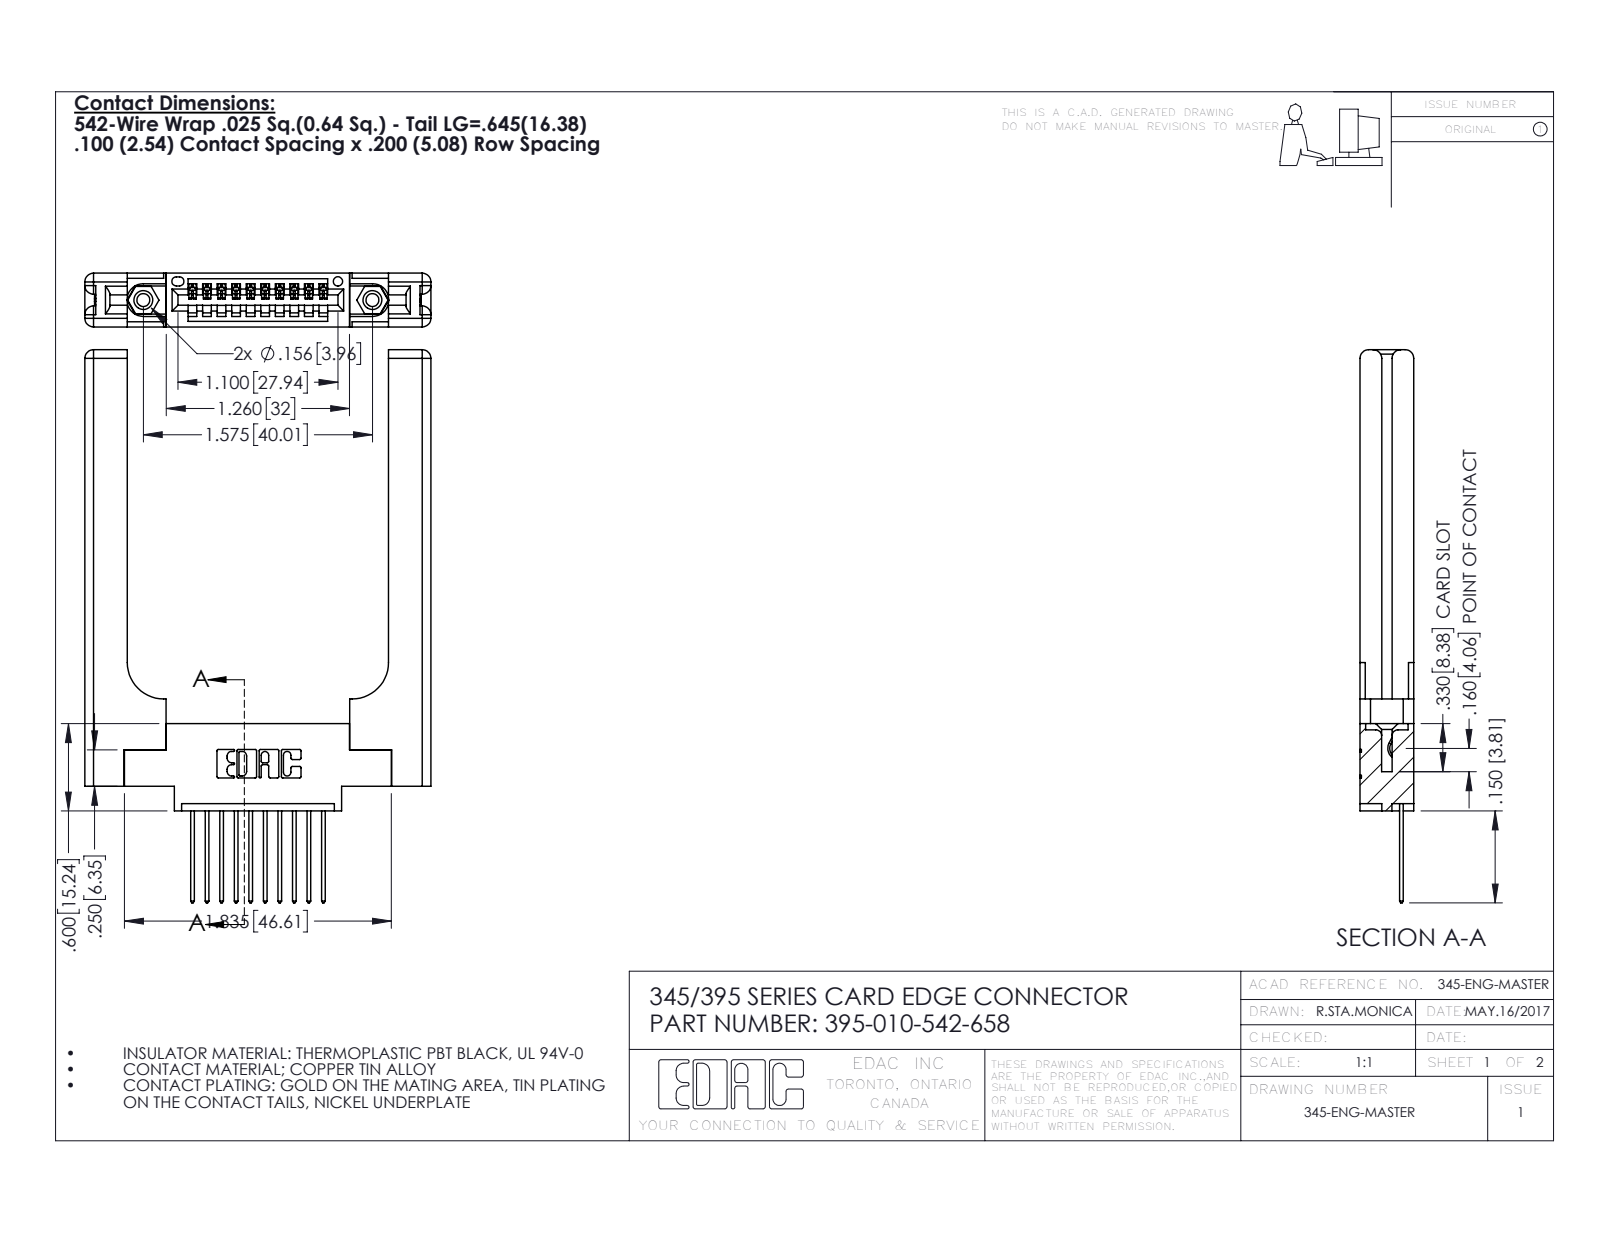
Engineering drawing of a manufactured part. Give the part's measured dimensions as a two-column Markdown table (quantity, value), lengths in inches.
| quantity | value |
| --- | --- |
| part name | 345-250-001_345-250-001-102; 395-010-542-658; 345 Part_0.170 Offset - 0.156 Dia-TH; 345-220-058_345-220-058 (+1 more) |
| STEP written by | SolidWorks 2016 (CONFIG_CONTROL_DESIGN) |
| units | inches |
| bodies | 15 solids, 966 faces (632 planar, 274 cylindrical, 60 other) |
| overall size | 3.802 × 2.379 × 0.37 |
| volume | 0.848 in³ |
| surface area | 19.06 in² |
| round holes (diameter × count) | 0.089 × 2, 0.125 × 2, 0.156 × 2, 0.064 × 1 |
| round bosses / shafts (diameter × count) | 0.155 × 2 |
| partial cylindrical surfaces (radius × count) | 0.01 × 22, 0.006 × 20, 0.01 × 20, 0.06 × 16, 0.007 × 6, 0.031 × 6, 0.026 × 3, 0.03 × 2 |
| main face-to-face distances | 0.37, 0.072, 0.15, 0.22, 0.298, 0.148, 0.077, 1.796, 0.12, 0.071 |
| hole center spacings | 0.27, 1.344, 1.575 |
